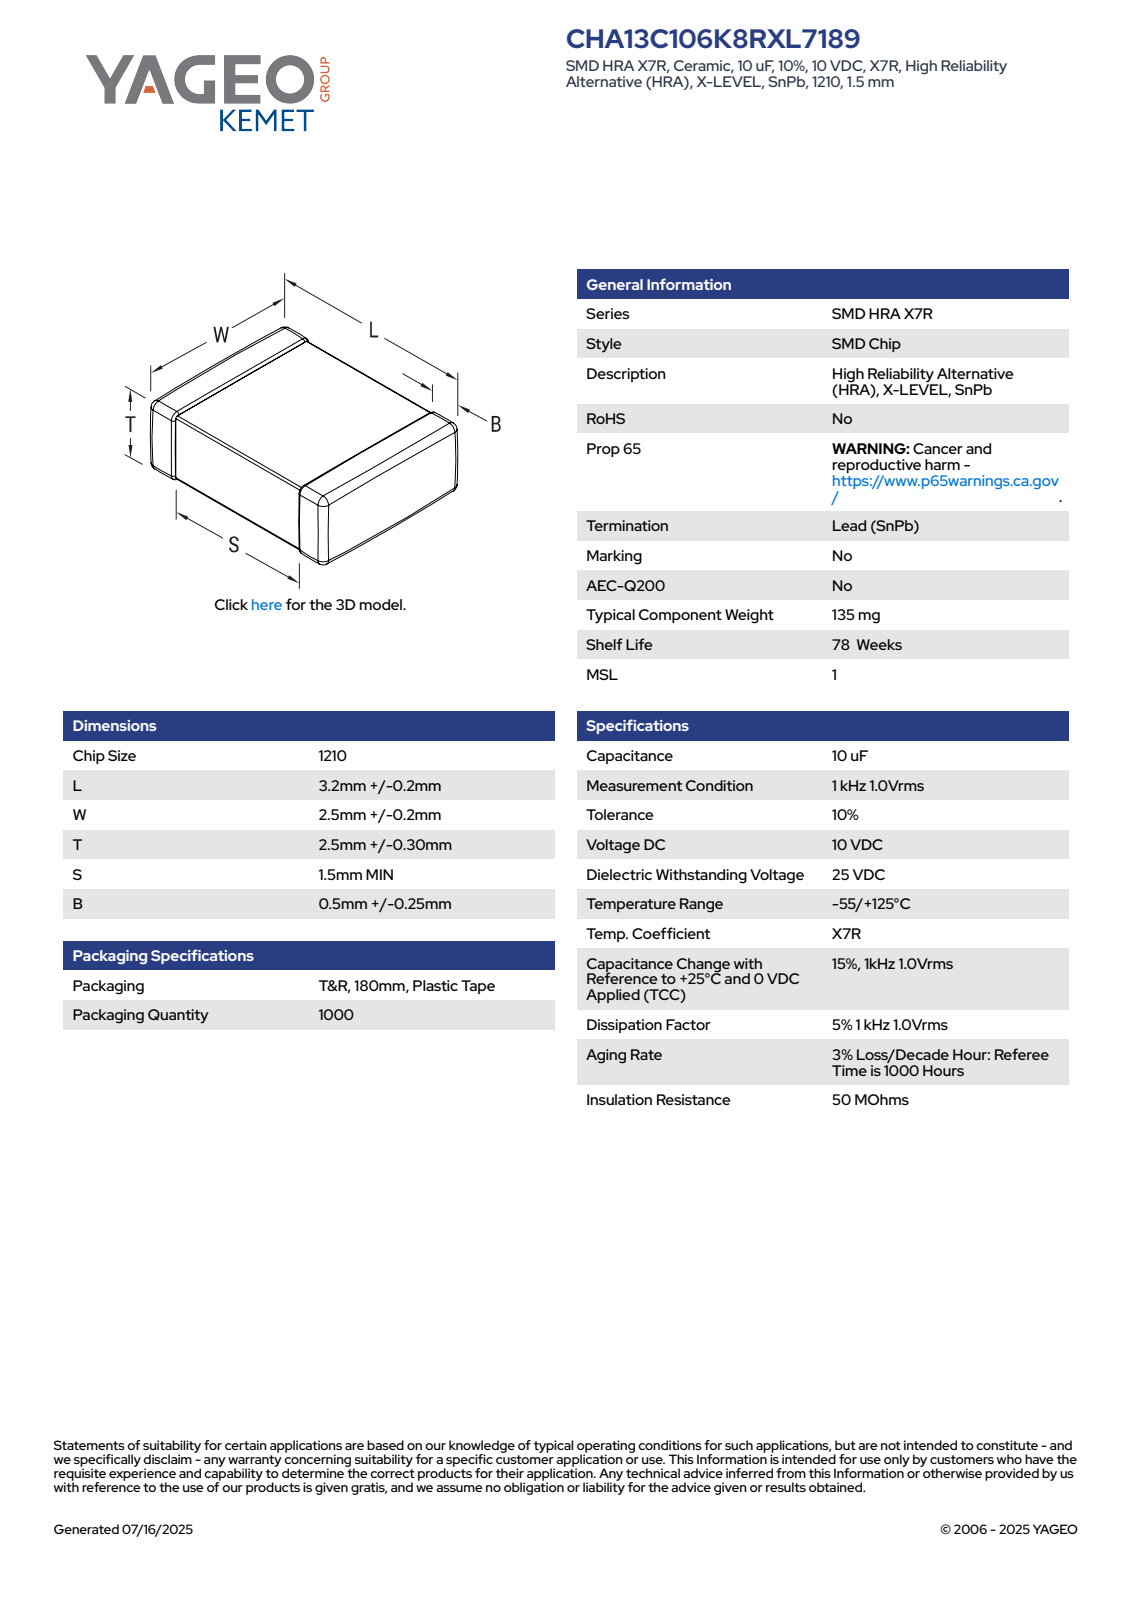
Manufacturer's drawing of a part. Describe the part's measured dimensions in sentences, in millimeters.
The part is named "CCSM_STD_1210_L3.4W2.7T2.8S2.5B0.75". Its 3-D file was written by "SolidWorks 2021 (AUTOMOTIVE_DESIGN)". It is 4 solids with 125 faces: 71 planar, 38 cylindrical and 16 other. Overall it measures 3.4 by 2.8 by 2.7 millimeters. Its volume is 25 cubic millimeters and its surface area 52 square millimeters. The main face-to-face distances are 3.4, 2.64, 2.74, 2.58, 2.68, 2.7, 2.8, 2.75, 2.69, 0.4.
